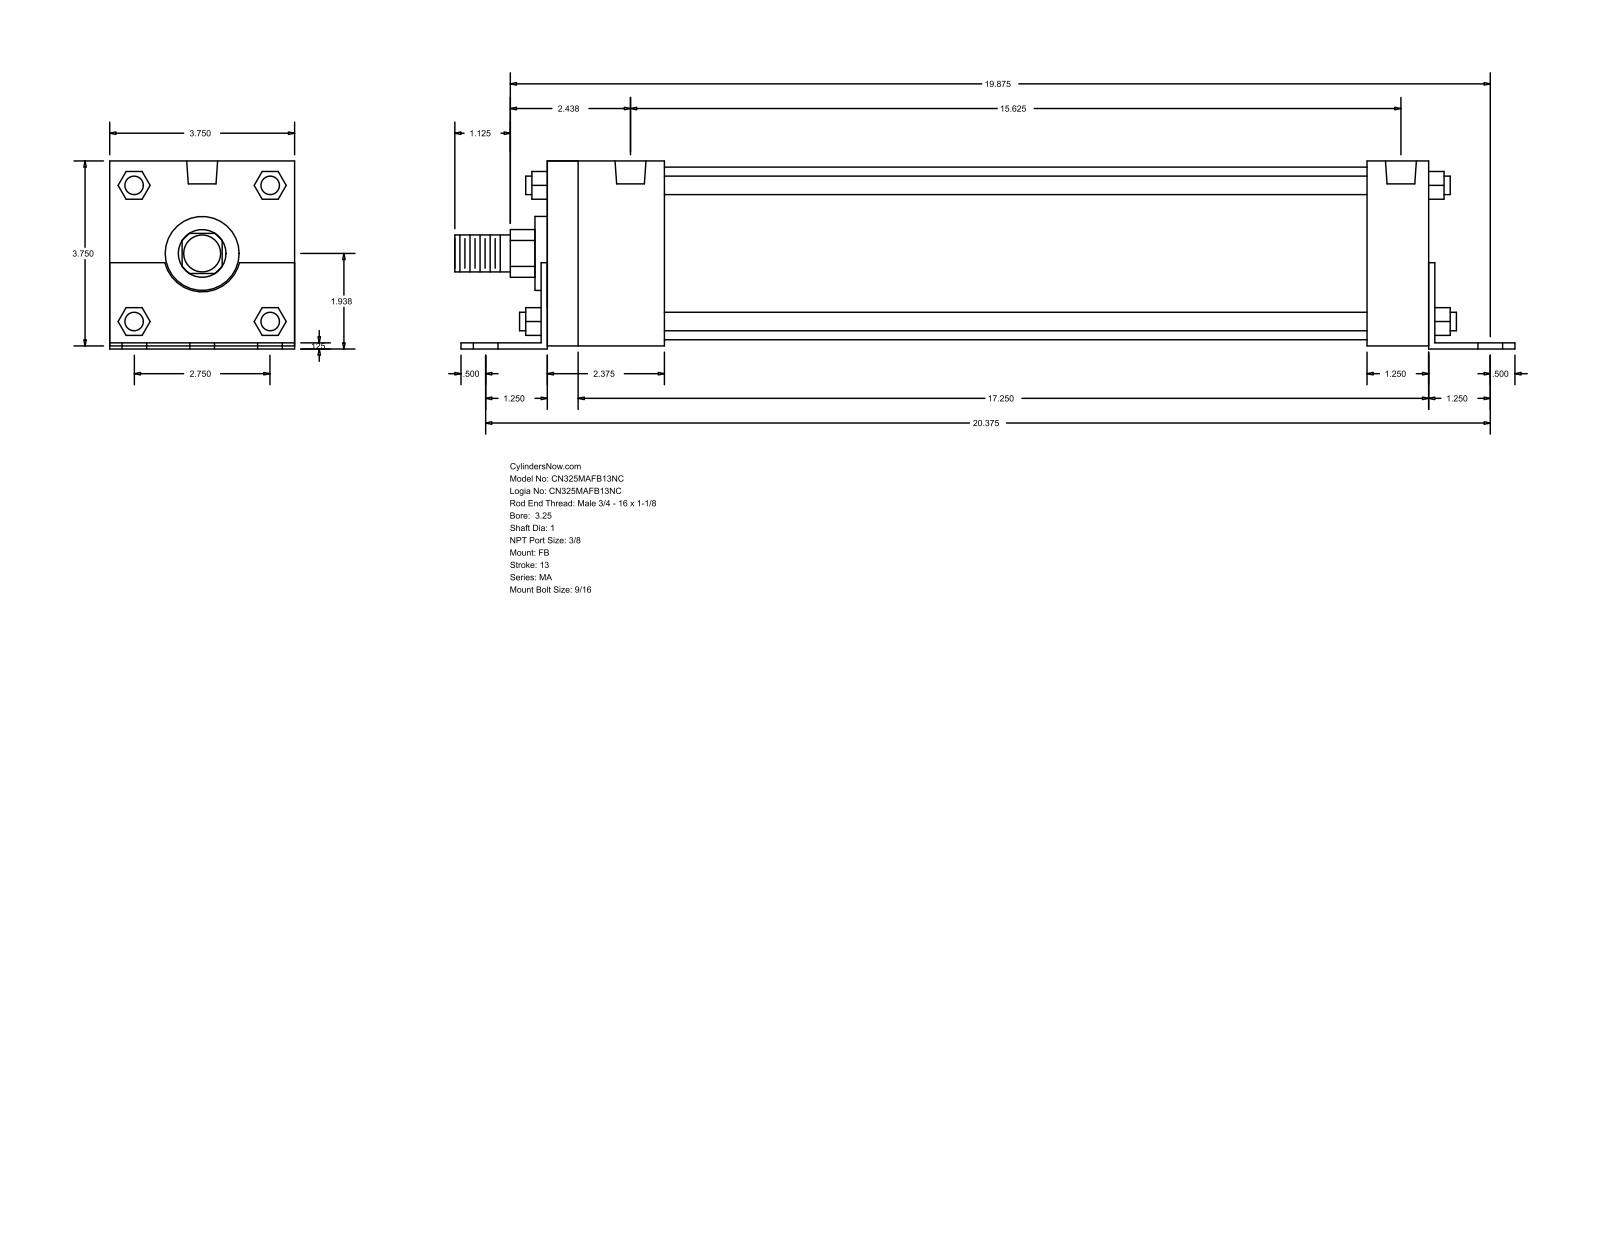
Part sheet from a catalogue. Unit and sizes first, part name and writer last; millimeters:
Units: millimetres
Overall size (bounding box): 546.1 × 96.84 × 95.25
Round holes (diameter × count): ⌀14.29 ×6, ⌀11.11 ×4, ⌀15.93 ×2
Round bosses / shafts (diameter × count): ⌀9.53 ×4, ⌀88.9 ×1, ⌀38.1 ×1, ⌀25.4 ×1, ⌀19.05 ×1
Partial cylindrical surfaces — rounded edges, fillets, slot ends (radius × count): R12.29 ×1, R19.81 ×1
Main face-to-face distances: 95.24, 3.17, 1.59, 96.83, 1.58, 93.66, 3.18, 454.02, 460.37, 457.2
Hole centre spacings: 34.92, 518.7, 517.52, 57.78, 61.64, 69.84, 82.38, 86.71
Bodies: 0 solids, 140 faces (105 planar, 35 cylindrical, 0 other)
Part name (STEP PRODUCT): MA_FB__0325_1
STEP written by: GSSL Pune (CONFIG_CONTROL_DESIGN)
